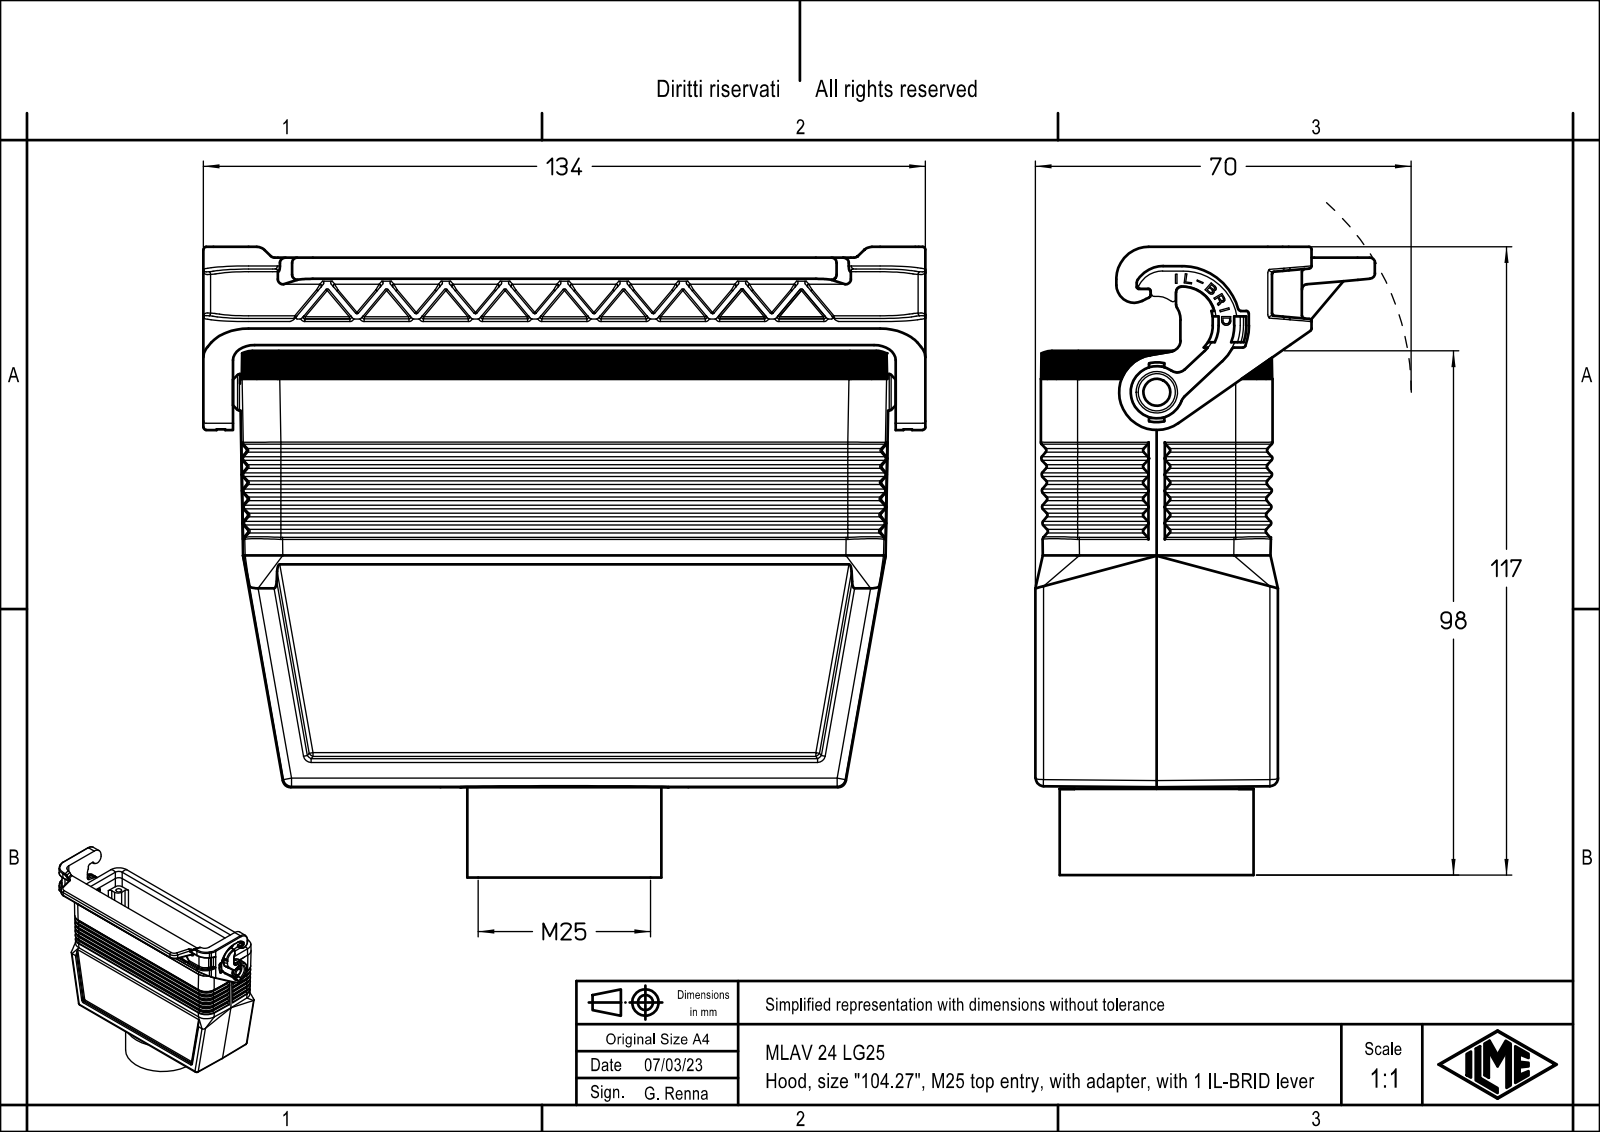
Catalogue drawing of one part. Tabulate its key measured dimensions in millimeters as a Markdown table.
| quantity | value |
| --- | --- |
| part name | MLAV 24 LG40; MLAV 24 LG25 |
| STEP written by | Creo Elements/Direct Modeling 20.1B 02-Apr-2019 (C) Parametric Technology GmbH (AUTOMOTIVE_DESIGN) |
| units | millimeters |
| bodies | 1 solid, 1373 faces (800 planar, 373 cylindrical, 200 other) |
| overall size | 134 × 119.25 × 63 |
| volume | 140 535 mm³ |
| surface area | 75 537 mm² |
| round holes (diameter × count) | 3 × 4, 3.5 × 4, 3.25 × 1, 5.4 × 1, 7.7 × 1, 23.5 × 1 |
| round bosses / shafts (diameter × count) | 32 × 1, 6.9 × 1, 6.8 × 1, 5.2 × 1, 3.2 × 1 |
| partial cylindrical surfaces (radius × count) | 0.5 × 77, 0.1 × 27, 1.5 × 23, 1 × 16, 0.2 × 15, 7 × 14, 0.33 × 13, 0.55 × 12 |
| main face-to-face distances | 3.75, 39.25, 35.5, 43, 2, 7, 46.25, 3.25, 42.5, 1 |
| hole center spacings | 53.72, 27, 104, 107.45 |
